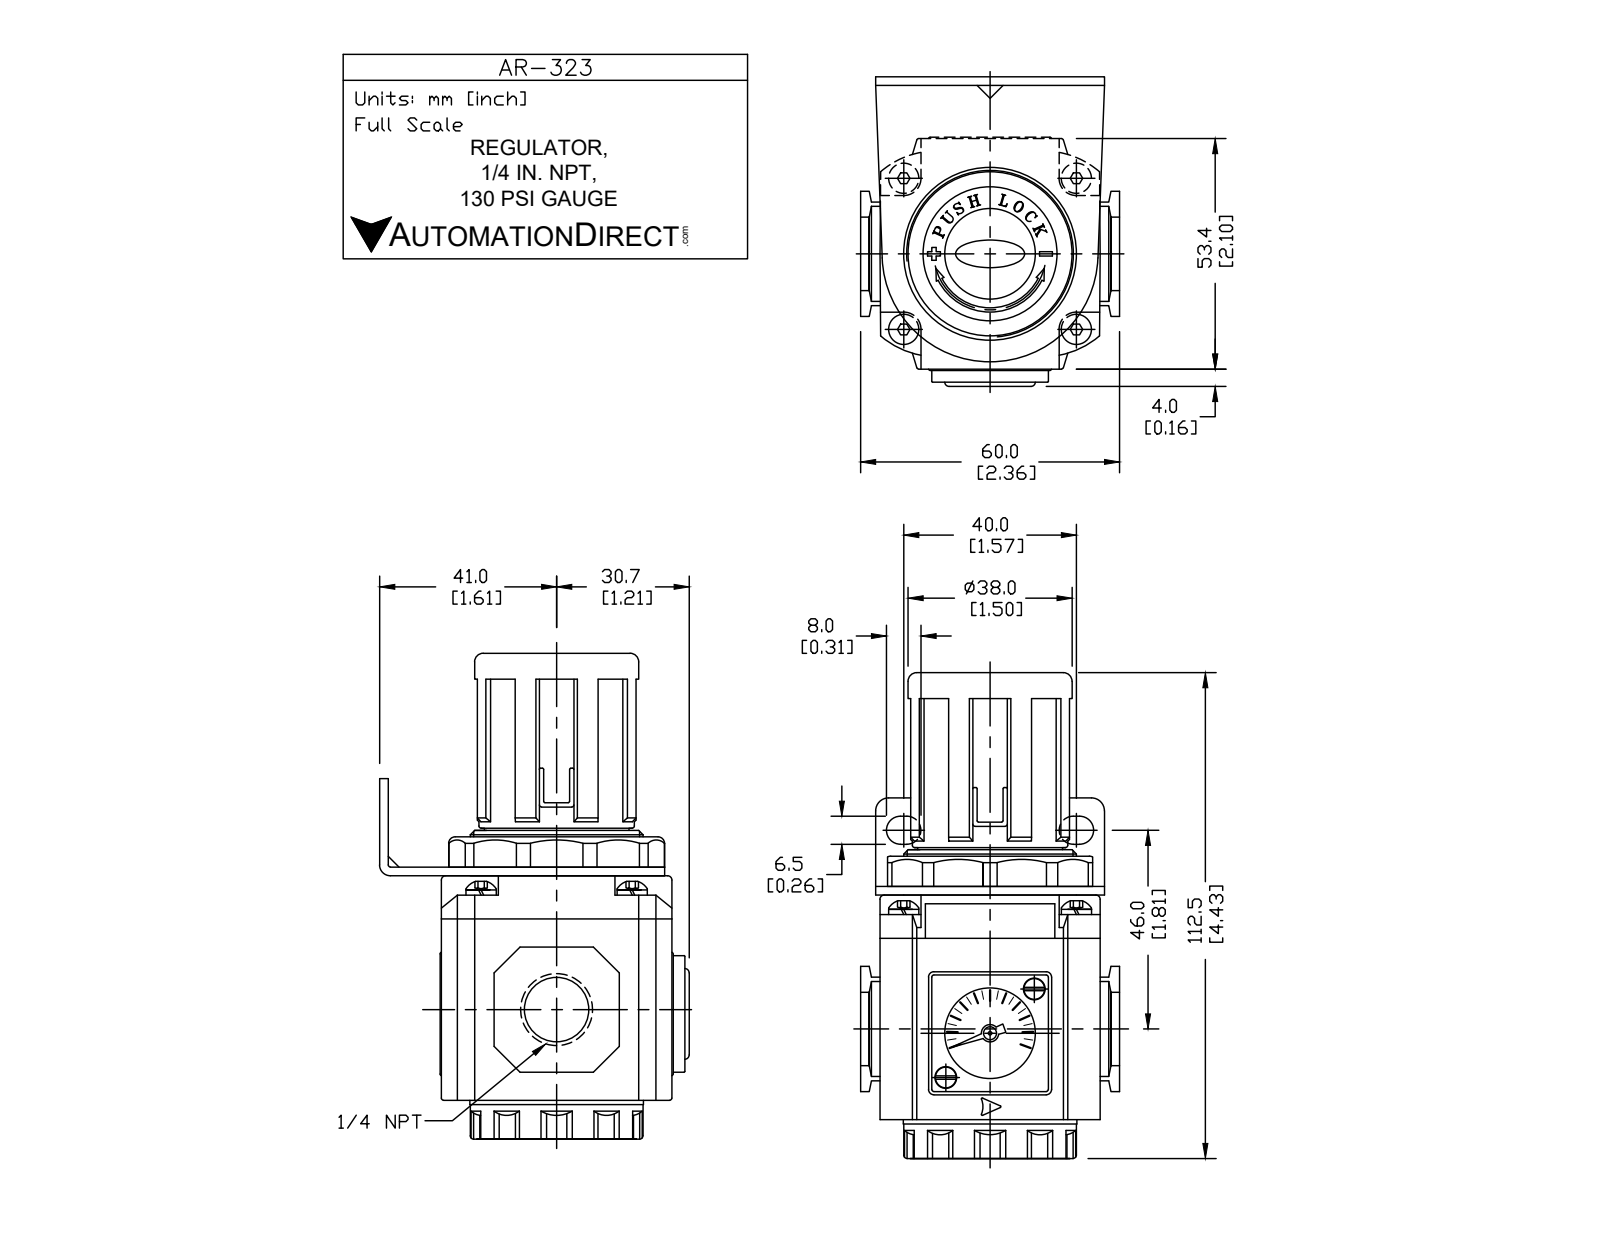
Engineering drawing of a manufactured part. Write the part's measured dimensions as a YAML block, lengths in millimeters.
part_name: "AR-323"
step_written_by: "SolidWorks 2015 (CONFIG_CONTROL_DESIGN)"
units: millimeters
bodies: {solids: 14, faces: 501, planar: 326, cylindrical: 133, other: 42}
overall_size: [112.5, 70.7, 60]
volume: 210579
surface_area: 43611
round_holes:
  - {diameter: 3, count: 6}
  - {diameter: 2, count: 1}
  - {diameter: 11.13, count: 1}
  - {diameter: 21, count: 1}
  - {diameter: 30, count: 1}
  - {diameter: 32, count: 1}
round_bosses_or_shafts:
  - {diameter: 5.5, count: 4}
  - {diameter: 2.7, count: 2}
  - {diameter: 40, count: 1}
  - {diameter: 39.2, count: 1}
  - {diameter: 38, count: 1}
  - {diameter: 33.5, count: 1}
  - {diameter: 20.46, count: 1}
  - {diameter: 4, count: 1}
partial_cylinders:
  - {radius: 1, count: 12}
  - {radius: 1.2, count: 10}
  - {radius: 3.25, count: 6}
  - {radius: 4, count: 5}
  - {radius: 0.3, count: 4}
  - {radius: 19.9, count: 4}
  - {radius: 0.2, count: 3}
  - {radius: 2, count: 1}
face_to_face_distances: [2, 52, 54, 53.4, 1, 9, 61, 55.5, 51, 52.4]
hole_center_spacings: [26.58, 14.5, 35, 40, 53.15, 28.99]
